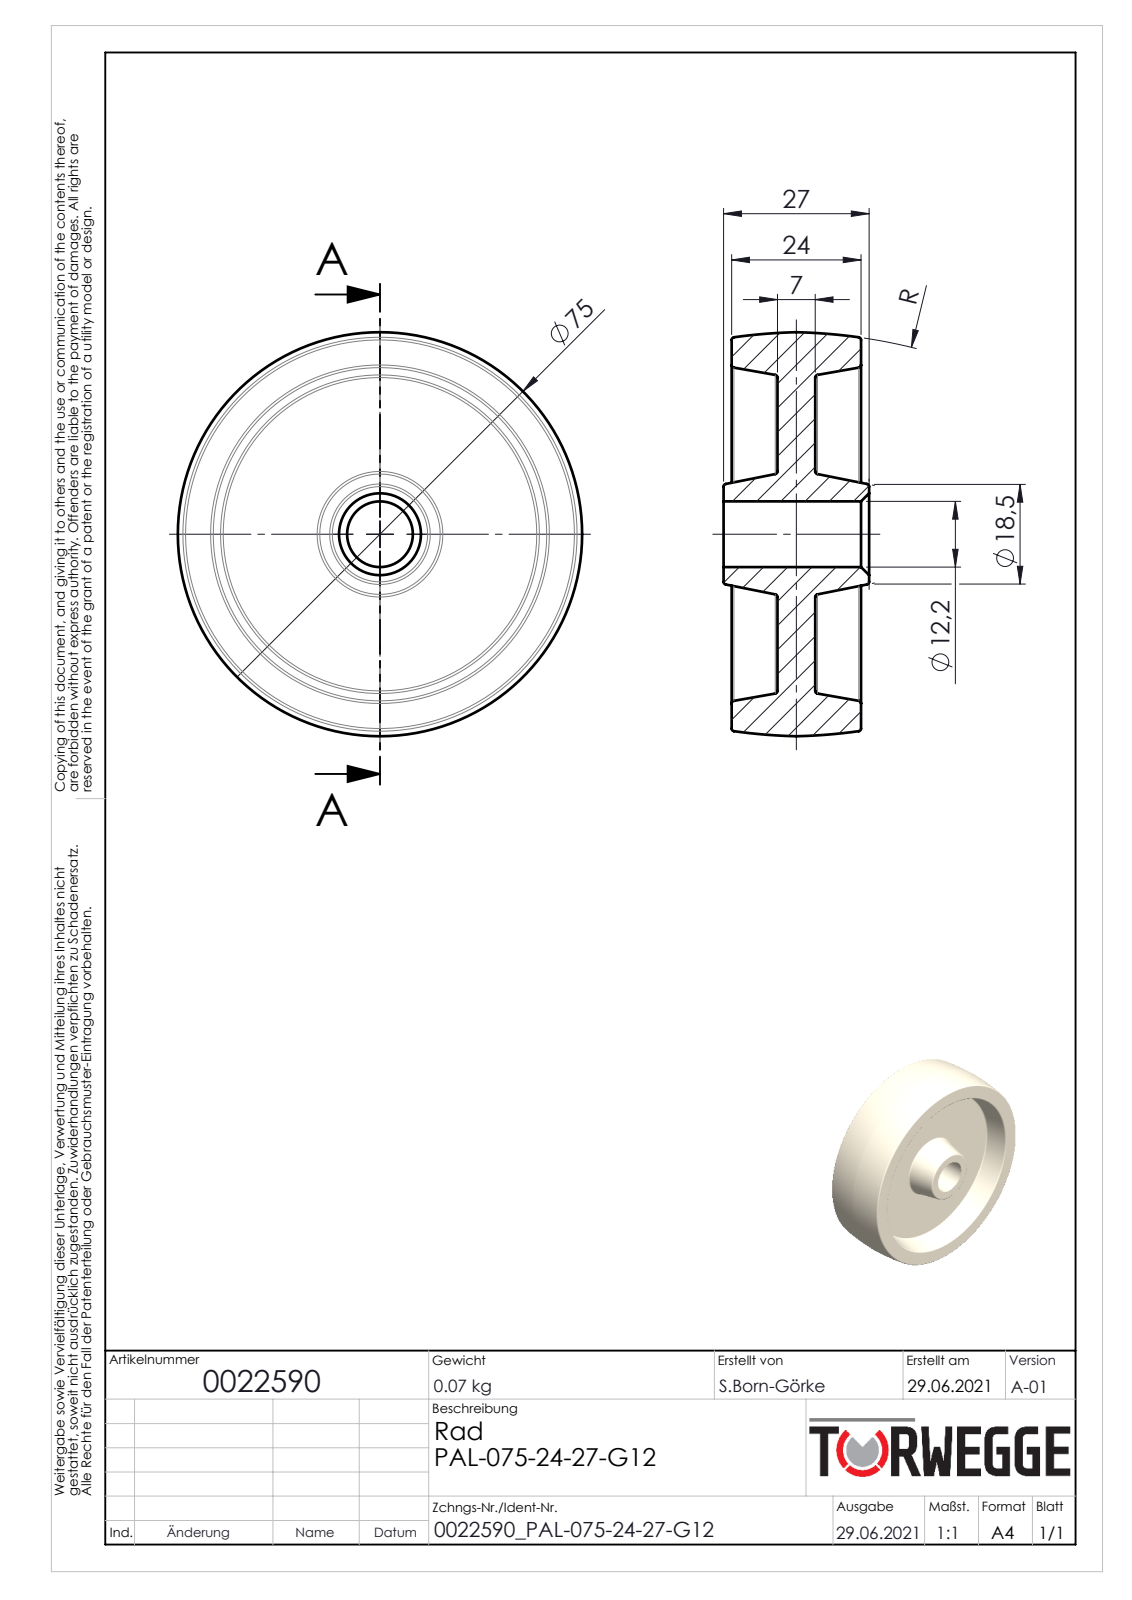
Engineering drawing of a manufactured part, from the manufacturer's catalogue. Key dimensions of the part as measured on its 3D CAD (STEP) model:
Part name (STEP PRODUCT): 0022590
STEP written by: SolidWorks 2020 (AUTOMOTIVE_DESIGN)
Units: millimetres
Bodies: 1 solid, 42 faces (6 planar, 2 cylindrical, 34 other)
Overall size (bounding box): 75 × 75 × 27
Volume: 58 426 mm³ · Surface area: 18 316 mm²
Round holes (diameter × count): ⌀12.2 ×1
Main face-to-face distances: 7, 8.5, 15.5, 24, 1.5, 10, 17, 25.5, 27
